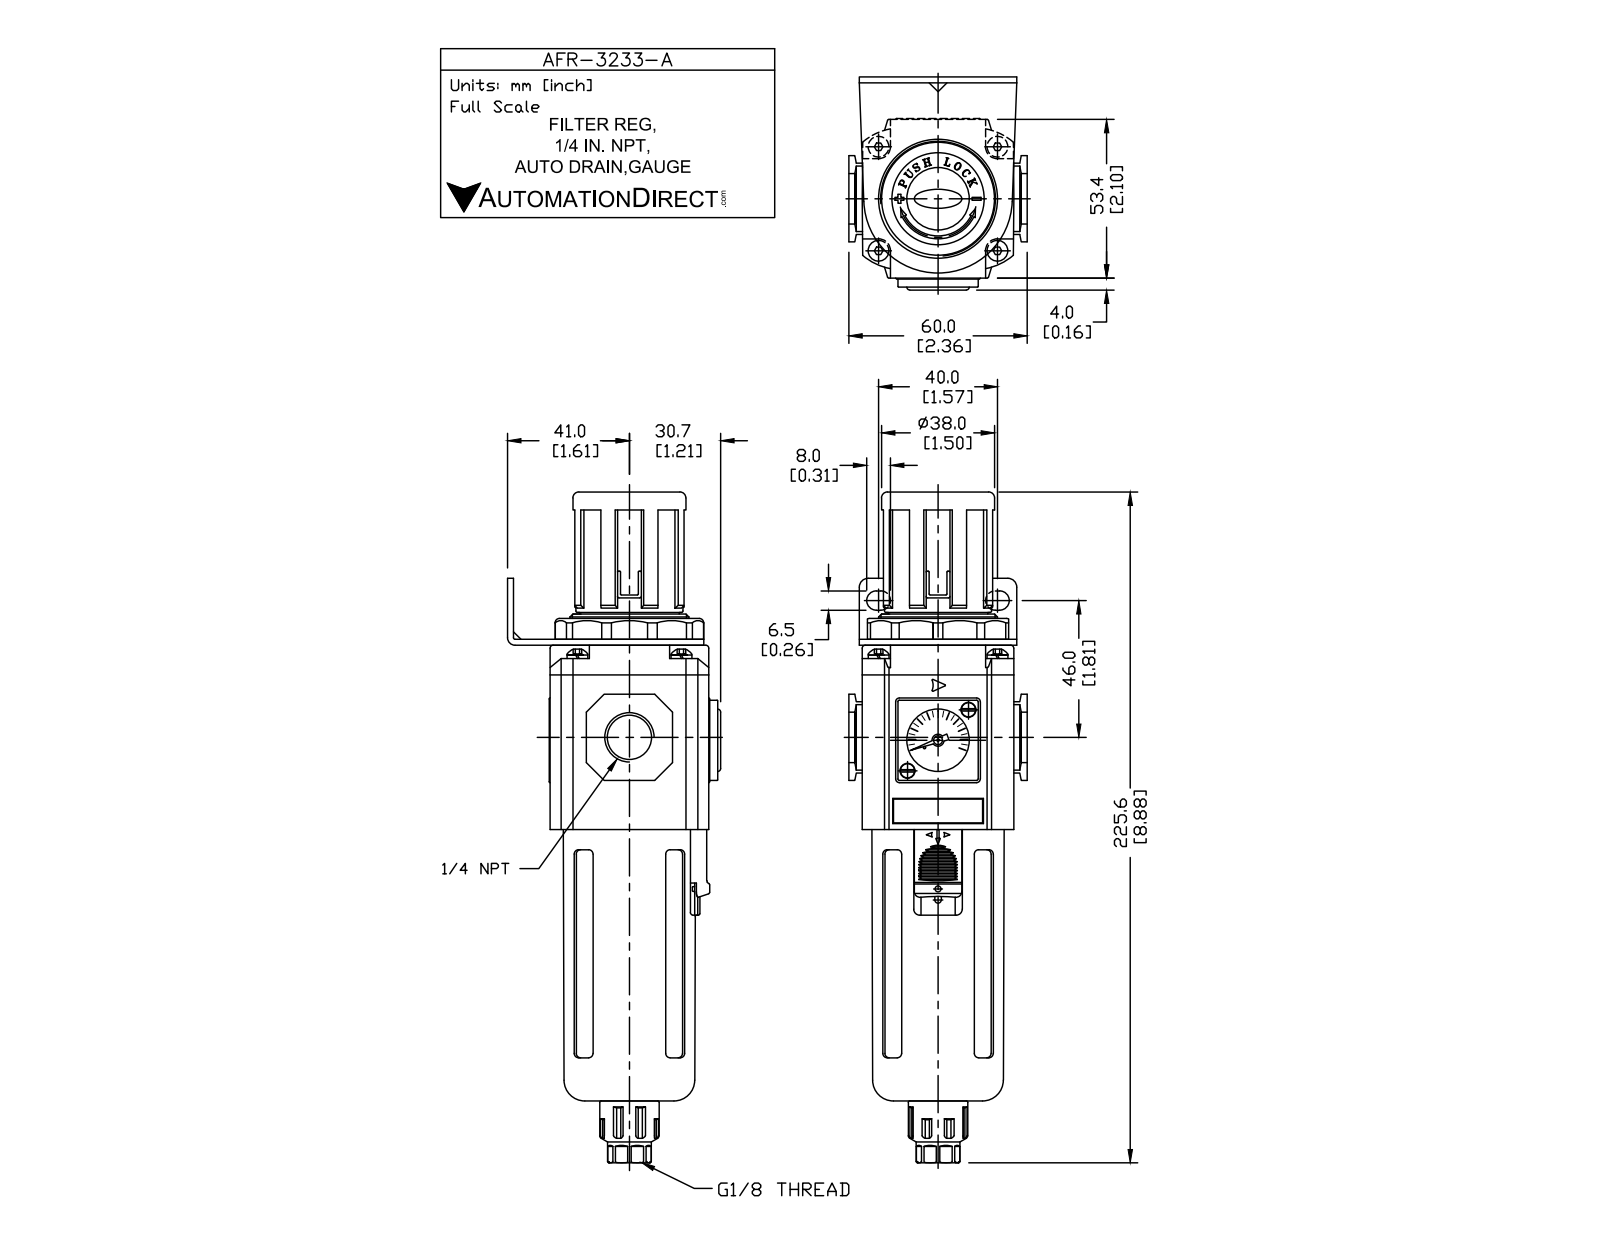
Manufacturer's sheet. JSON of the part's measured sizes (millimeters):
{"part_name": "AFR-3233-A", "step_written_by": "SolidWorks 2015 (CONFIG_CONTROL_DESIGN)", "units": "millimeters", "bodies": {"solids": 16, "faces": 606, "planar": 370, "cylindrical": 172, "other": 64}, "overall_size": [225.6, 72, 60], "volume_mm3": 276308, "surface_area_mm2": 69828, "round_holes": [[3, 6], [2, 1], [6.2, 1], [11.13, 1], [16, 1], [21, 1], [30, 1], [32, 1], [35.2, 1]], "round_bosses_or_shafts": [[5.5, 4], [2.7, 2], [44, 1], [40, 1], [38, 1], [36, 1], [33.5, 1], [20.46, 1]], "partial_cylinders_radius": [[2.2, 18], [1, 12], [1.2, 10], [0.5, 8], [9.5, 8], [3.25, 6], [4, 5], [0.3, 4]], "face_to_face_distances": [2, 62, 64, 53.4, 51, 39.6, 1, 55.5, 52.4, 4.5], "hole_center_spacings": [26.58, 14.5, 35, 40, 53.15, 28.99]}
